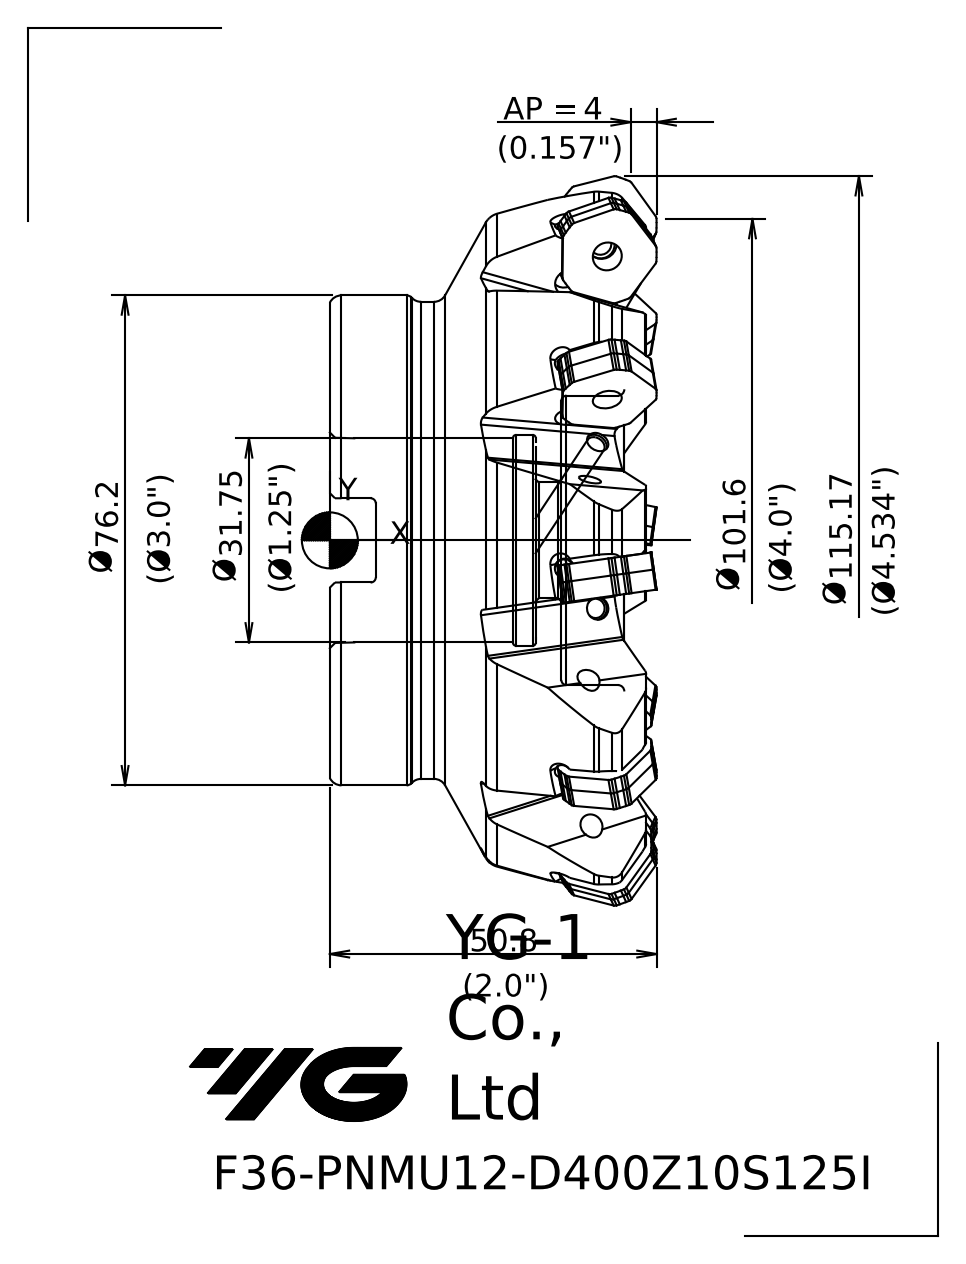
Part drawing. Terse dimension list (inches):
name: 120185C07CB1h80d
written by: SIEMENS PLM Software NX 10.0 (AP203_CONFIGURATION_CONTROLLED_3D_DESIGN_OF_MECHANICAL_PARTS_AND_ASSEMBLIES_MIM_LF)
unit: in
bodies: 1 solid, 70 faces (19 planar, 9 cylindrical, 42 other)
size: 4.534 × 4.534 × 2
volume: 18.06 in³; area: 59.43 in²
holes: 1× ⌀0.709, 1× ⌀1.25, 1× ⌀1.289
bosses: 1× ⌀3, 1× ⌀2.921
rounds: 2× R0.031
face distances: 1.77, 0.337, 1.433, 0.352, 0.015, 1.417, 0.51, 0.173, 0.157, 1.26
